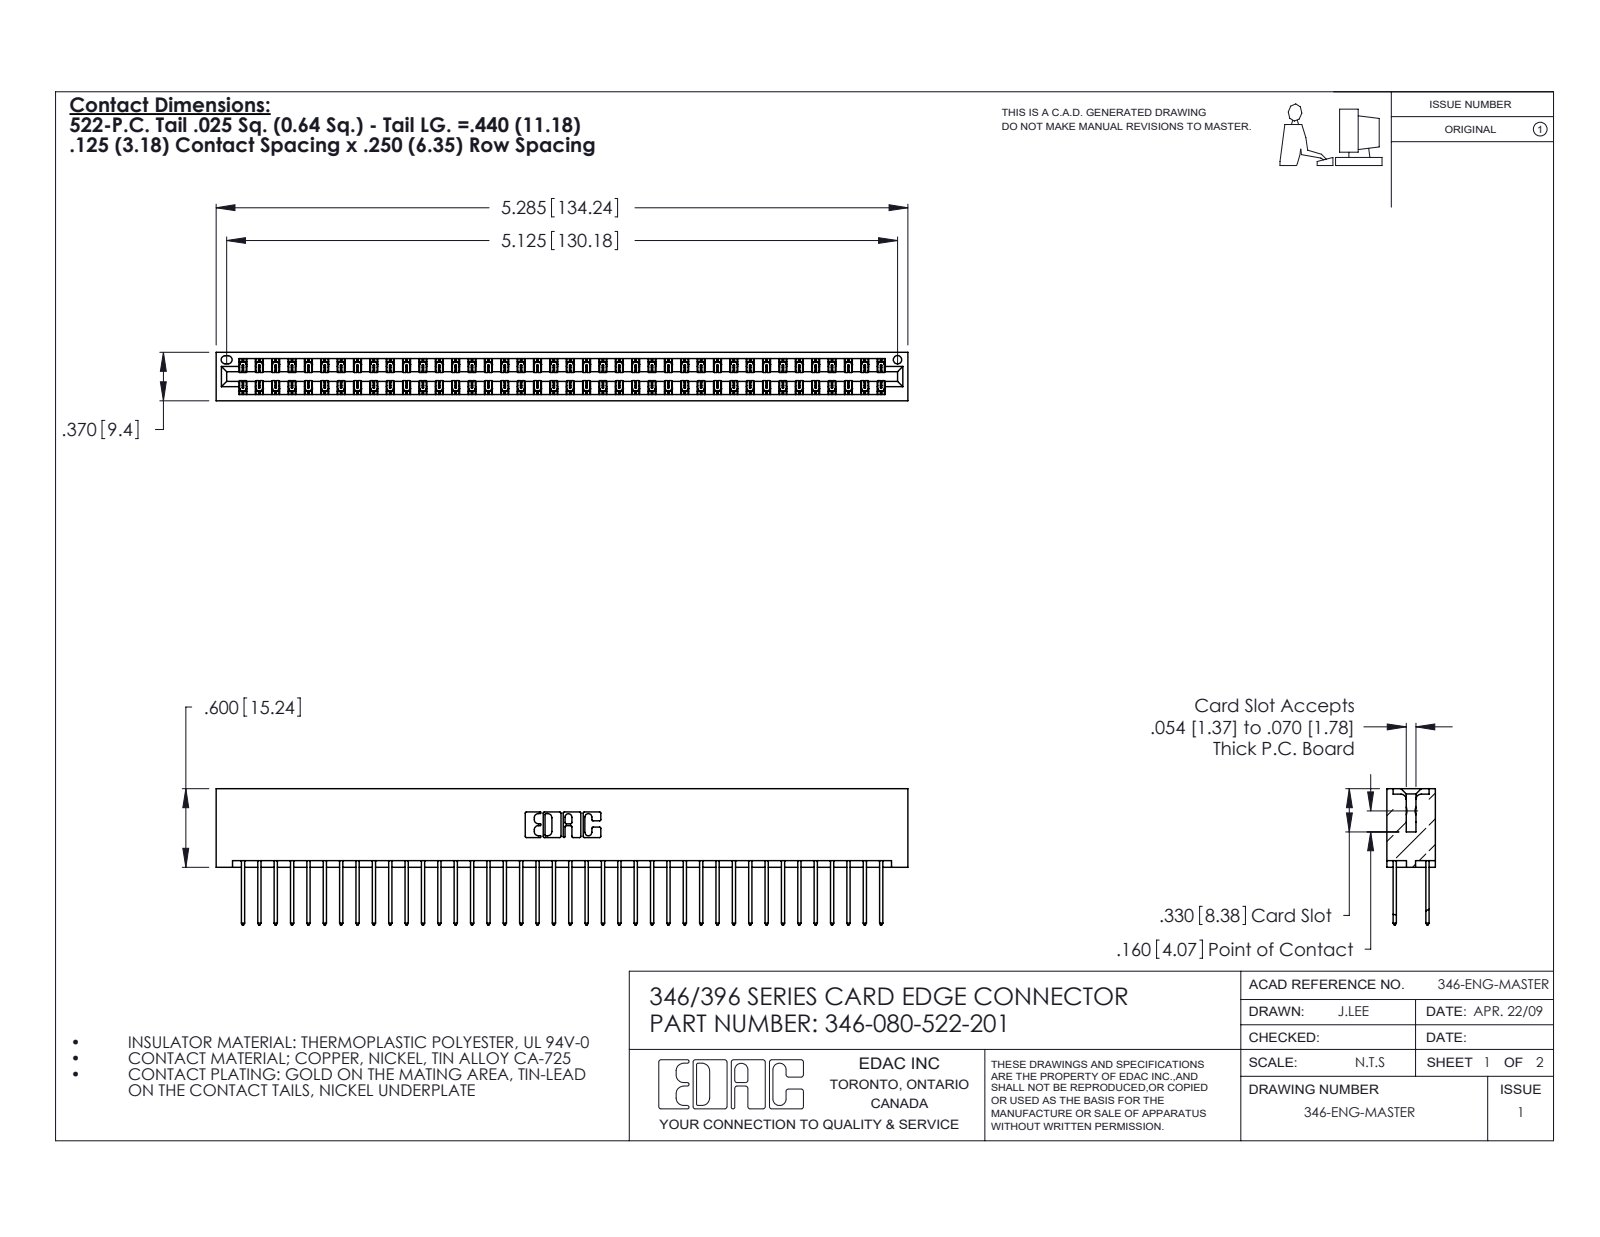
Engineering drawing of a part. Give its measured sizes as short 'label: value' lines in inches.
name: 345-292-001_345-293-122; 346 Part_No Mounting Lugs; 346-080-522-201
written by: SolidWorks 2020 (CONFIG_CONTROL_DESIGN)
unit: in
bodies: 81 solids, 4274 faces (2872 planar, 1402 cylindrical, 0 other)
size: 5.285 × 1.04 × 0.37
volume: 0.845 in³; area: 31.19 in²
holes: 1× ⌀0.064
rounds: 120× R0.006, 80× R0.01, 22× R0.01, 6× R0.007, 6× R0.031, 3× R0.026, 2× R0.014, 2× R0.022
face distances: 0.048, 0.322, 0.25, 0.072, 0.298, 0.025, 0.37, 0.275, 0.148, 0.222
